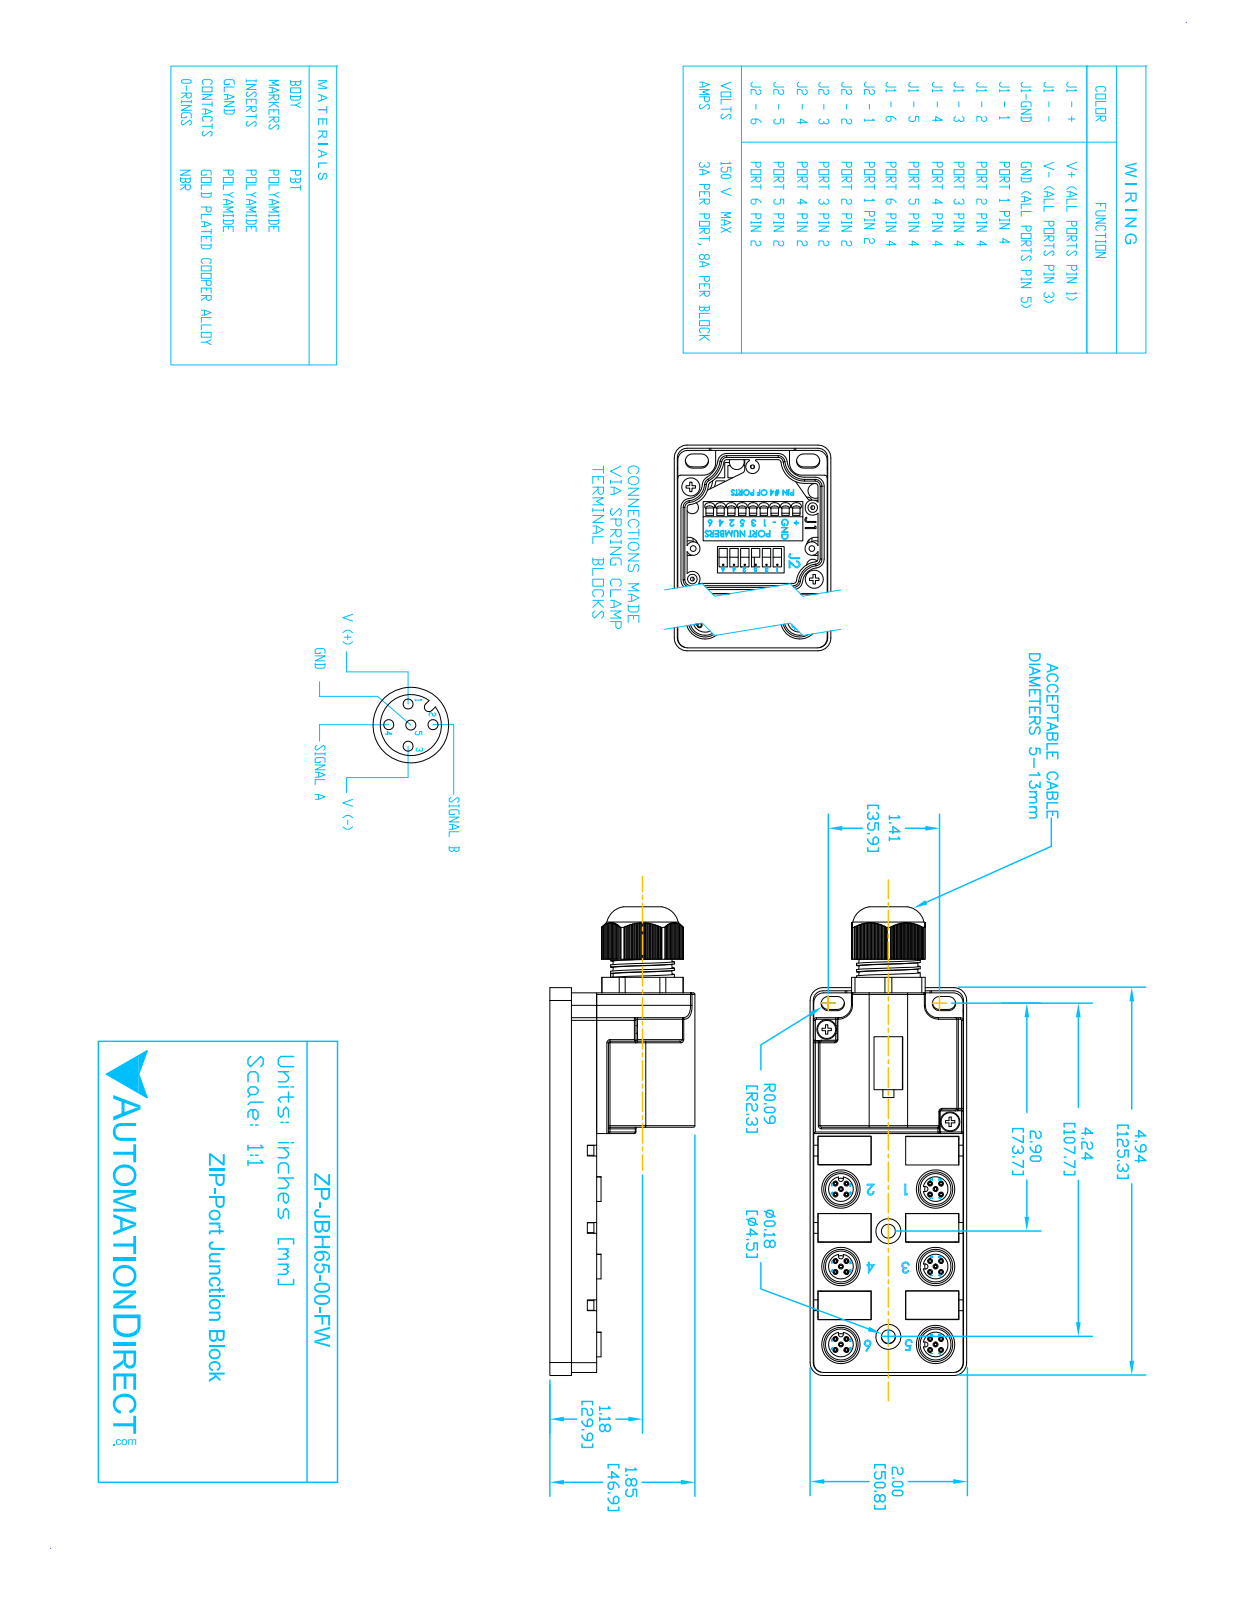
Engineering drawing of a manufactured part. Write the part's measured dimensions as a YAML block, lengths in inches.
part_name: "ZP-JBH64-00-FW"
step_written_by: "SolidWorks 2016 (AUTOMOTIVE_DESIGN)"
units: inches
bodies: {solids: 8, faces: 1402, planar: 799, cylindrical: 388, other: 215}
overall_size: [5.963, 1.991, 1.846]
volume: 8.885
surface_area: 59.55
round_holes:
  - {diameter: 0.043, count: 30}
  - {diameter: 0.063, count: 30}
  - {diameter: 0.093, count: 8}
  - {diameter: 0.437, count: 6}
  - {diameter: 0.488, count: 6}
  - {diameter: 0.177, count: 2}
  - {diameter: 0.25, count: 2}
  - {diameter: 0.26, count: 2}
  - {diameter: 0.318, count: 2}
  - {diameter: 0.05, count: 1}
  - {diameter: 0.37, count: 1}
  - {diameter: 0.49, count: 1}
round_bosses_or_shafts:
  - {diameter: 0.19, count: 7}
  - {diameter: 0.622, count: 4}
  - {diameter: 0.315, count: 4}
  - {diameter: 0.315, count: 2}
  - {diameter: 0.23, count: 2}
  - {diameter: 0.81, count: 1}
  - {diameter: 0.375, count: 1}
  - {diameter: 0.375, count: 1}
partial_cylinders:
  - {radius: 0.02, count: 34}
  - {radius: 0.09, count: 8}
  - {radius: 0.031, count: 6}
  - {radius: 0.046, count: 4}
  - {radius: 0.164, count: 4}
  - {radius: 0.035, count: 2}
  - {radius: 0.126, count: 2}
  - {radius: 0.156, count: 2}
face_to_face_distances: [0.596, 0.276, 0.32, 0.354, 0.078, 0.242, 1.9, 0.035, 0.313, 0.588]
hole_center_spacings: [0.098, 0.139, 1.135, 0.139, 0.92, 0.987, 1.203, 1.275]
